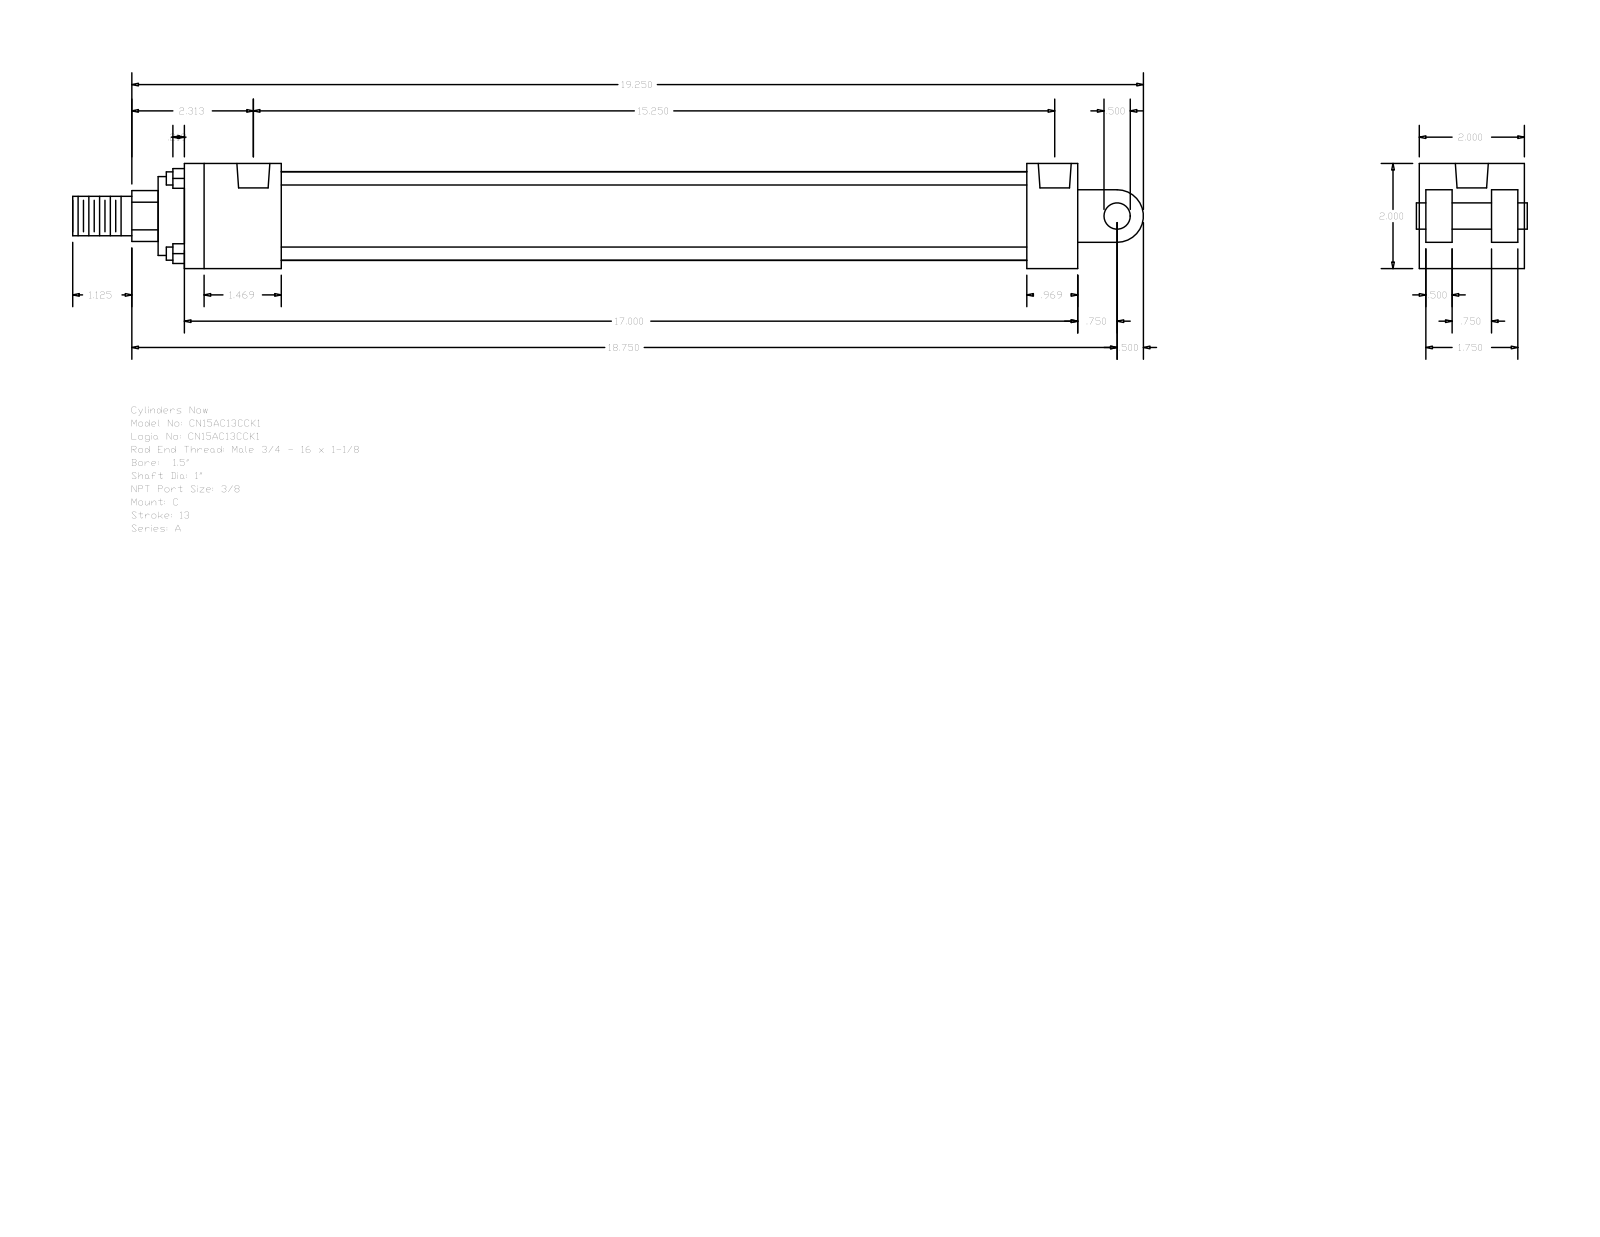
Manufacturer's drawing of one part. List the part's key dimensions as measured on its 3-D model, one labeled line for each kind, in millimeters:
Part name (STEP PRODUCT): A_C__0150_1
STEP written by: GSSL Pune (CONFIG_CONTROL_DESIGN)
Units: millimetres
Bodies: 0 solids, 99 faces (70 planar, 29 cylindrical, 0 other)
Overall size (bounding box): 517.52 × 50.8 × 50.8
Round holes (diameter × count): ⌀5.56 ×4, ⌀15.93 ×2
Round bosses / shafts (diameter × count): ⌀6.35 ×4, ⌀42.93 ×1, ⌀38.1 ×1, ⌀25.4 ×1, ⌀19.05 ×1, ⌀12.7 ×1
Partial cylindrical surfaces — rounded edges, fillets, slot ends (radius × count): R12.29 ×1, R12.7 ×1
Main face-to-face distances: 50.8, 12.7, 3.17, 15.87, 34.93, 47.63, 31.76, 431.8, 38.1, 407.19
Hole centre spacings: 3.97, 379.41, 383.38, 387.35
